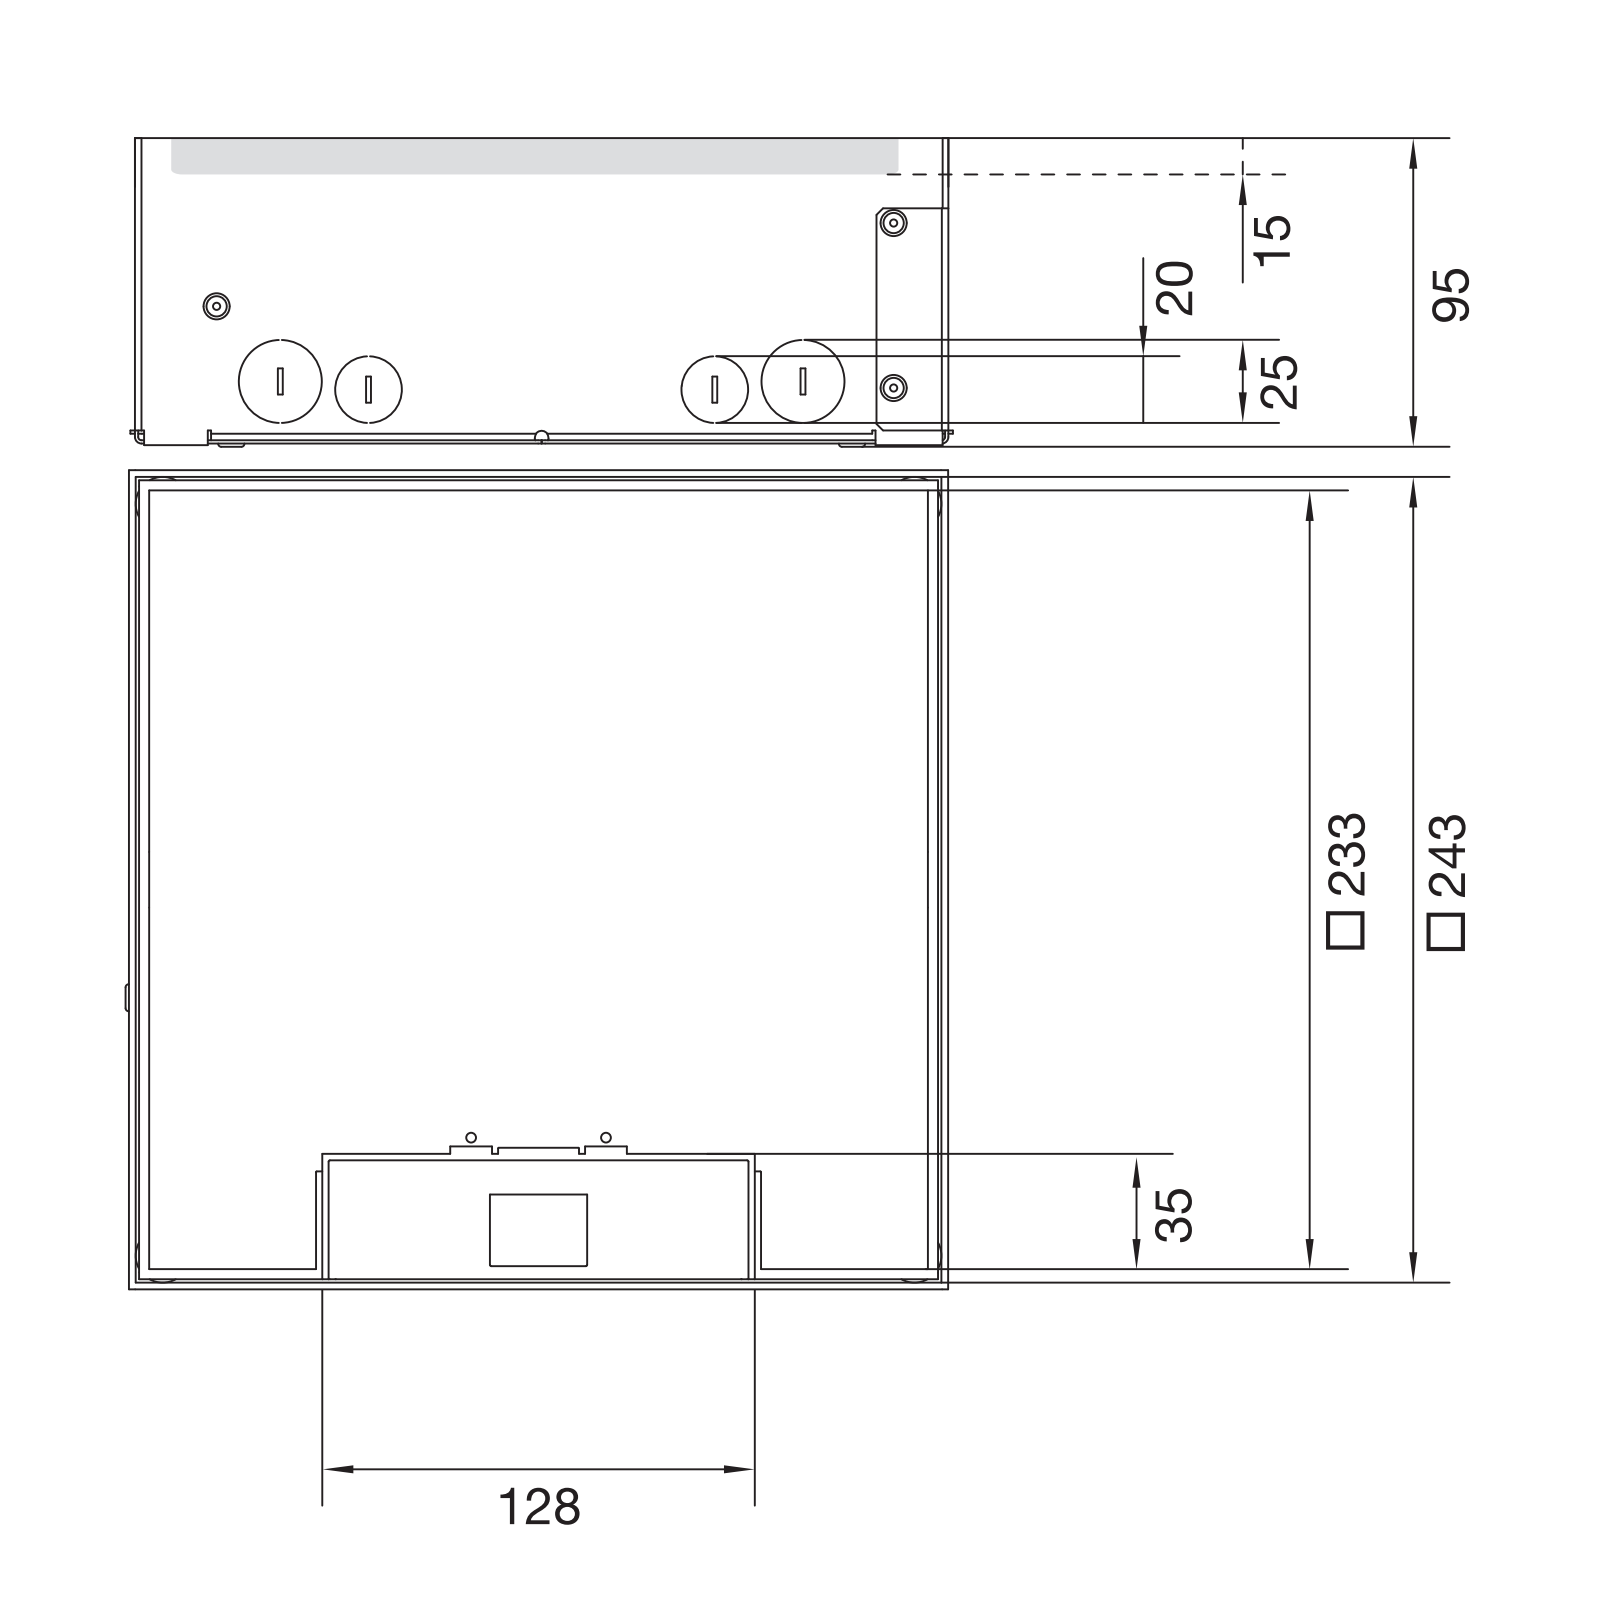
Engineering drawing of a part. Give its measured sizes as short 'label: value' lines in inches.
name: T-00659; 60449-M; 60450-M; T-00714 (+8 more)
written by: CREO PARAMETRIC BY PTC INC, 2022024 (AUTOMOTIVE_DESIGN)
unit: in
bodies: 25 solids, 1537 faces (1008 planar, 329 cylindrical, 200 other)
size: 9.813 × 9.803 × 3.681
volume: 34.39 in³; area: 1 192 in²
holes: 12× ⌀0.803, 8× ⌀1, 4× ⌀0.268, 4× ⌀0.295, 4× ⌀0.728, 2× ⌀0.106
bosses: 16× ⌀0.787, 8× ⌀0.984, 4× ⌀0.807, 4× ⌀0.472, 4× ⌀0.453, 4× ⌀0.388, 4× ⌀0.335, 4× ⌀0.315
rounds: 22× R0.039, 16× R0.197, 12× R0.118, 8× R0.083, 7× R0.079, 7× R0.089, 1× R0.26, 1× R5.906
face distances: 0.039, 0.079, 9.764, 3.012, 0.118, 0.197, 0.049, 2.972, 3.091, 3.051
hole spacings: 1.068, 4.574, 4.643, 5.237, 8.78, 1.072, 1.643, 1.67
